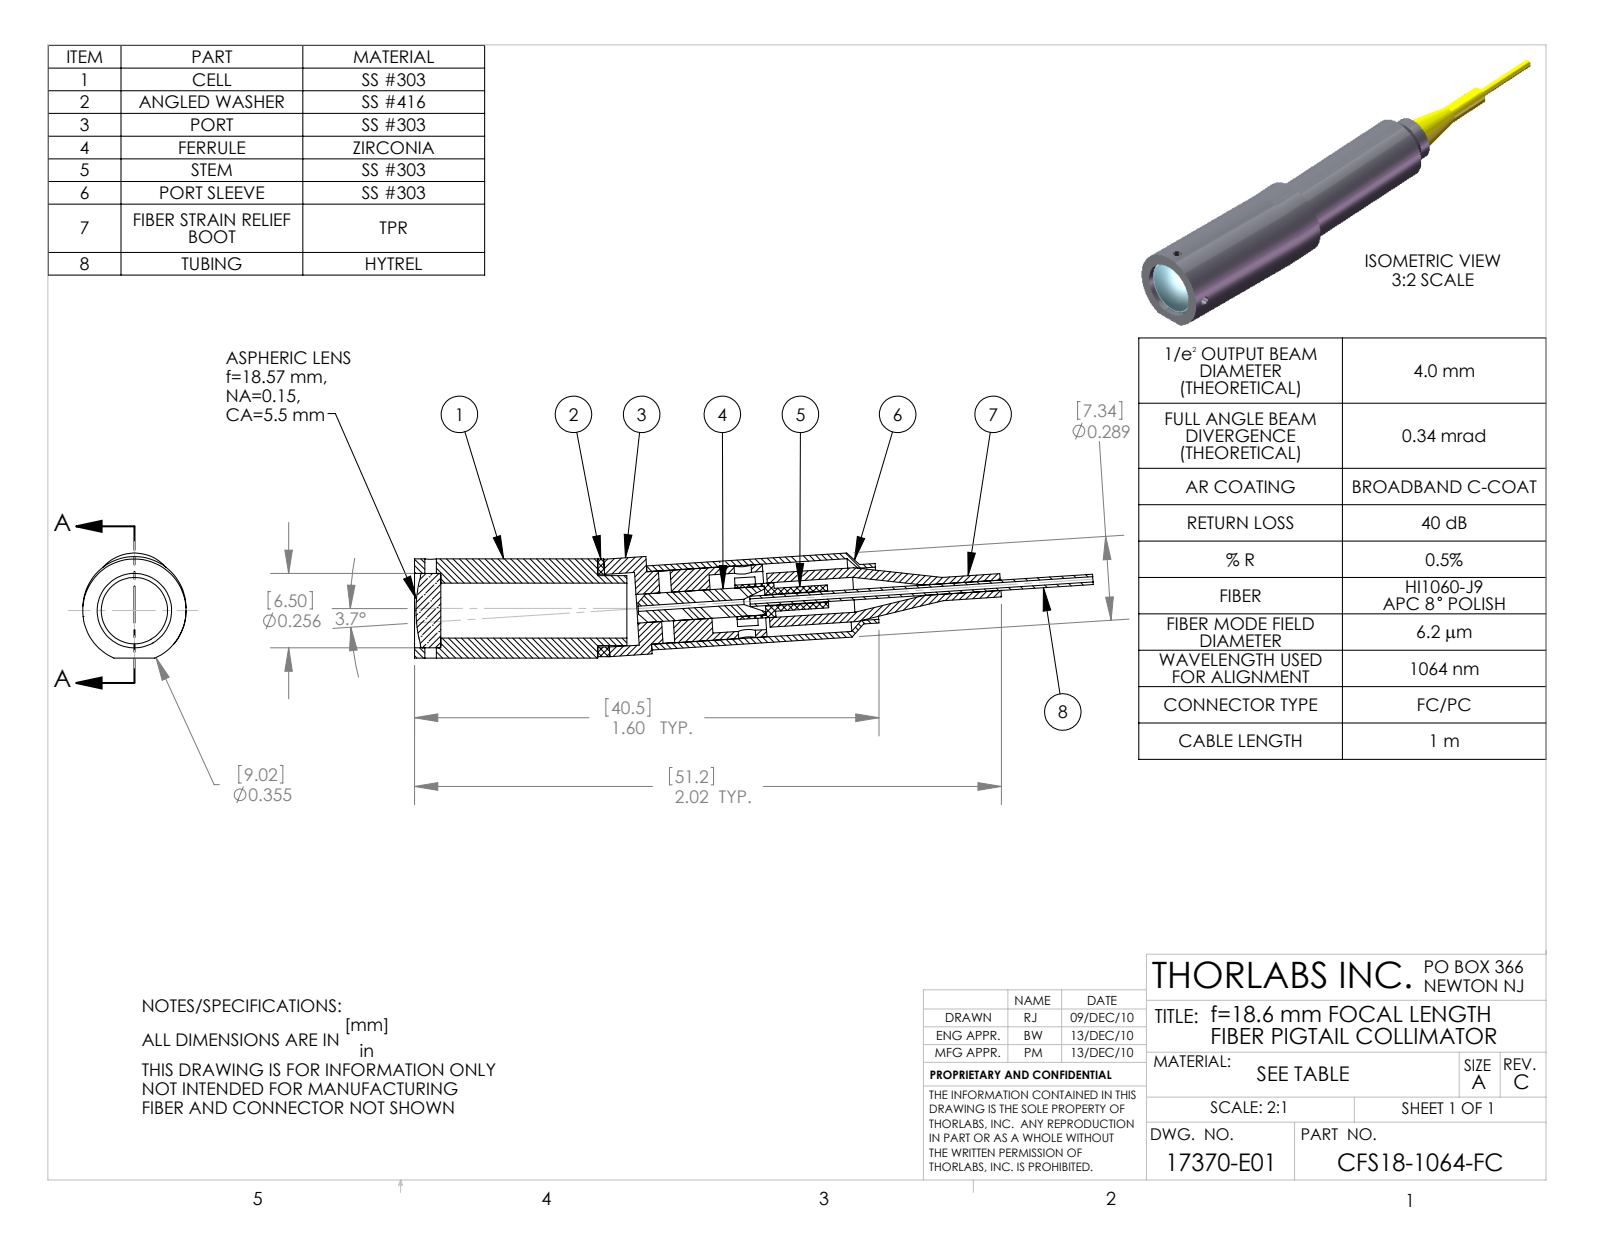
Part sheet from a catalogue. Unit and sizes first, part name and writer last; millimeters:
Units: millimetres
Overall size (bounding box): 59.25 × 9.16 × 9.02
Round holes (diameter × count): ⌀1.02 ×2, ⌀0.46 ×1, ⌀4.57 ×1, ⌀6.5 ×1
Round bosses / shafts (diameter × count): ⌀9.02 ×1, ⌀9 ×1, ⌀7.34 ×1, ⌀5.21 ×1, ⌀2.03 ×1, ⌀0.9 ×1
Main face-to-face distances: 3.68, 16, 23.62, 19.94, 34.44, 30.76, 10.82, 15.49, 0.51, 42.51
Bodies: 0 solids, 54 faces (13 planar, 31 cylindrical, 10 other)
Part name (STEP PRODUCT): 17370-E0W
STEP written by: SolidWorks 2009 (AUTOMOTIVE_DESIGN)
